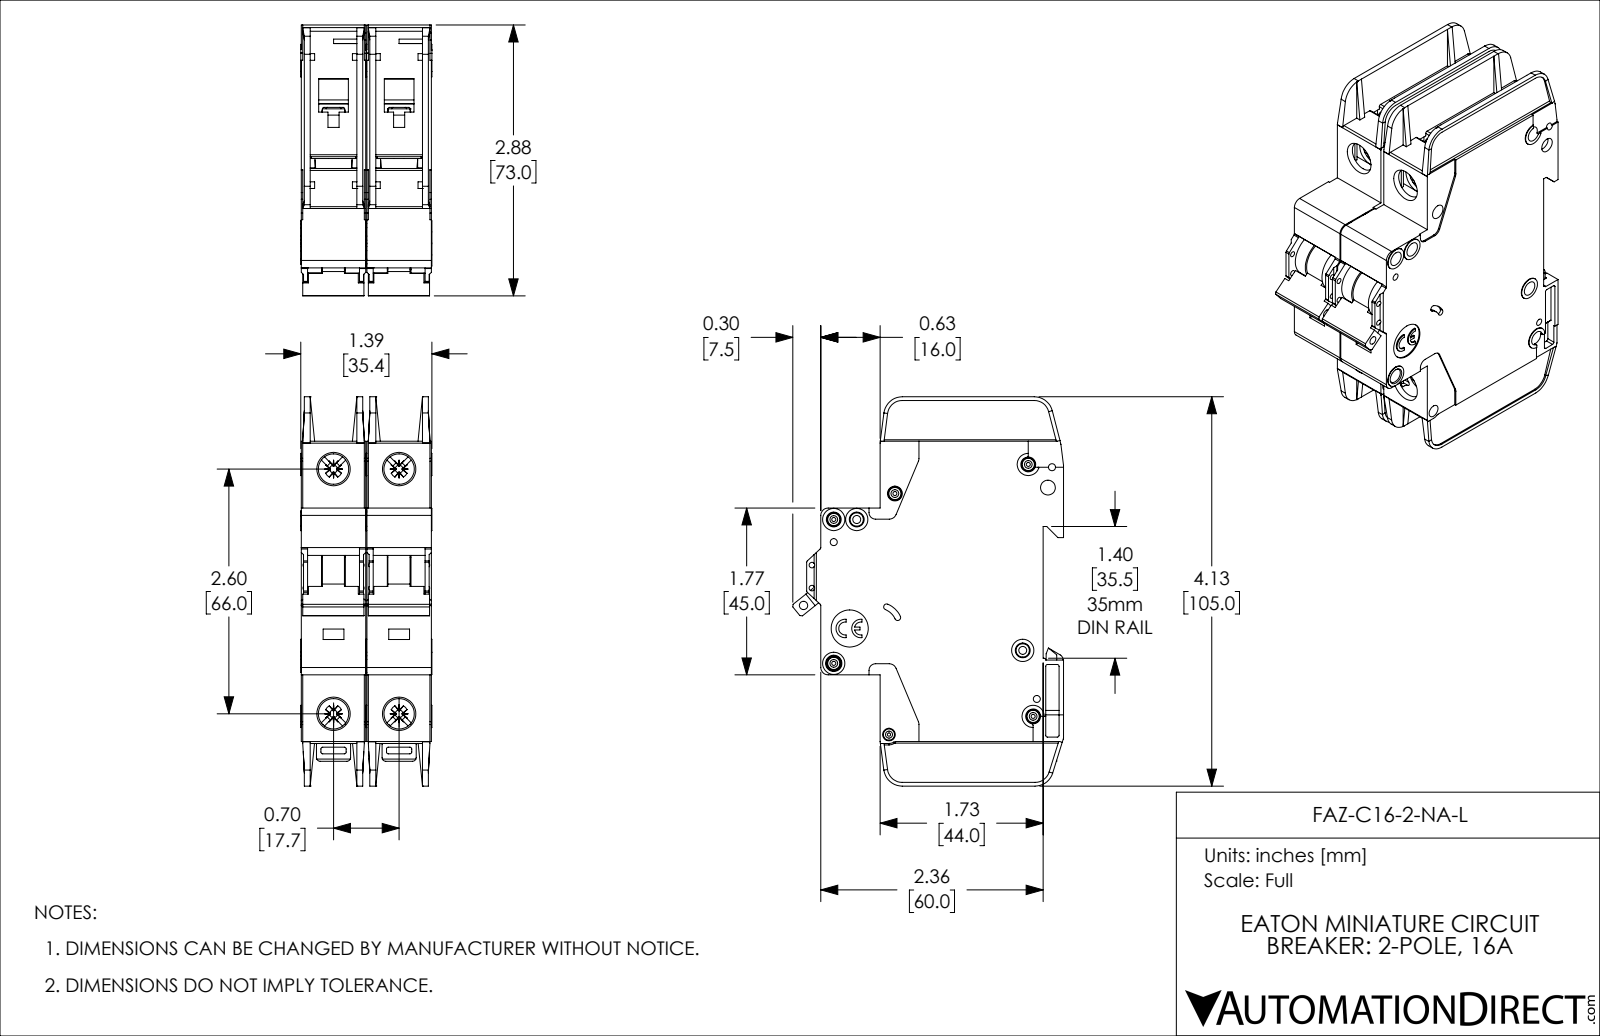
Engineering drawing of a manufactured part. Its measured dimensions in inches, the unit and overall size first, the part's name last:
Units: inches
Overall size (bounding box): 4.134 × 2.876 × 1.394
Round holes (diameter × count): ⌀0.157 ×8, ⌀0.043 ×5, ⌀0.075 ×4, ⌀0.323 ×4, ⌀0.059 ×2, ⌀0.085 ×2, ⌀0.035 ×1, ⌀0.089 ×1, ⌀0.098 ×1, ⌀0.134 ×1, ⌀0.394 ×1
Round bosses / shafts (diameter × count): ⌀0.13 ×5, ⌀0.236 ×4, ⌀0.118 ×3, ⌀0.098 ×2
Partial cylindrical surfaces — rounded edges, fillets, slot ends (radius × count): R0.02 ×57, R0.016 ×20, R0.039 ×14, R0.079 ×10, R0.043 ×8, R0.008 ×5, R0.197 ×5, R0.01 ×4
Main face-to-face distances: 0.697, 0.047, 0.685, 0.591, 0.094, 0.638, 0.543, 1.382, 0.744, 0.65
Hole centre spacings: 0.244, 0.537, 0.697, 0.87, 2.598, 2.69, 0.189, 0.199
Volume: 9.365 in³ · Surface area: 82.01 in²
Bodies: 2 solids, 2254 faces (1342 planar, 714 cylindrical, 198 other)
Part name (STEP PRODUCT): FAZ-C16-2-NA-L
STEP written by: SolidWorks 2019 (AUTOMOTIVE_DESIGN)
